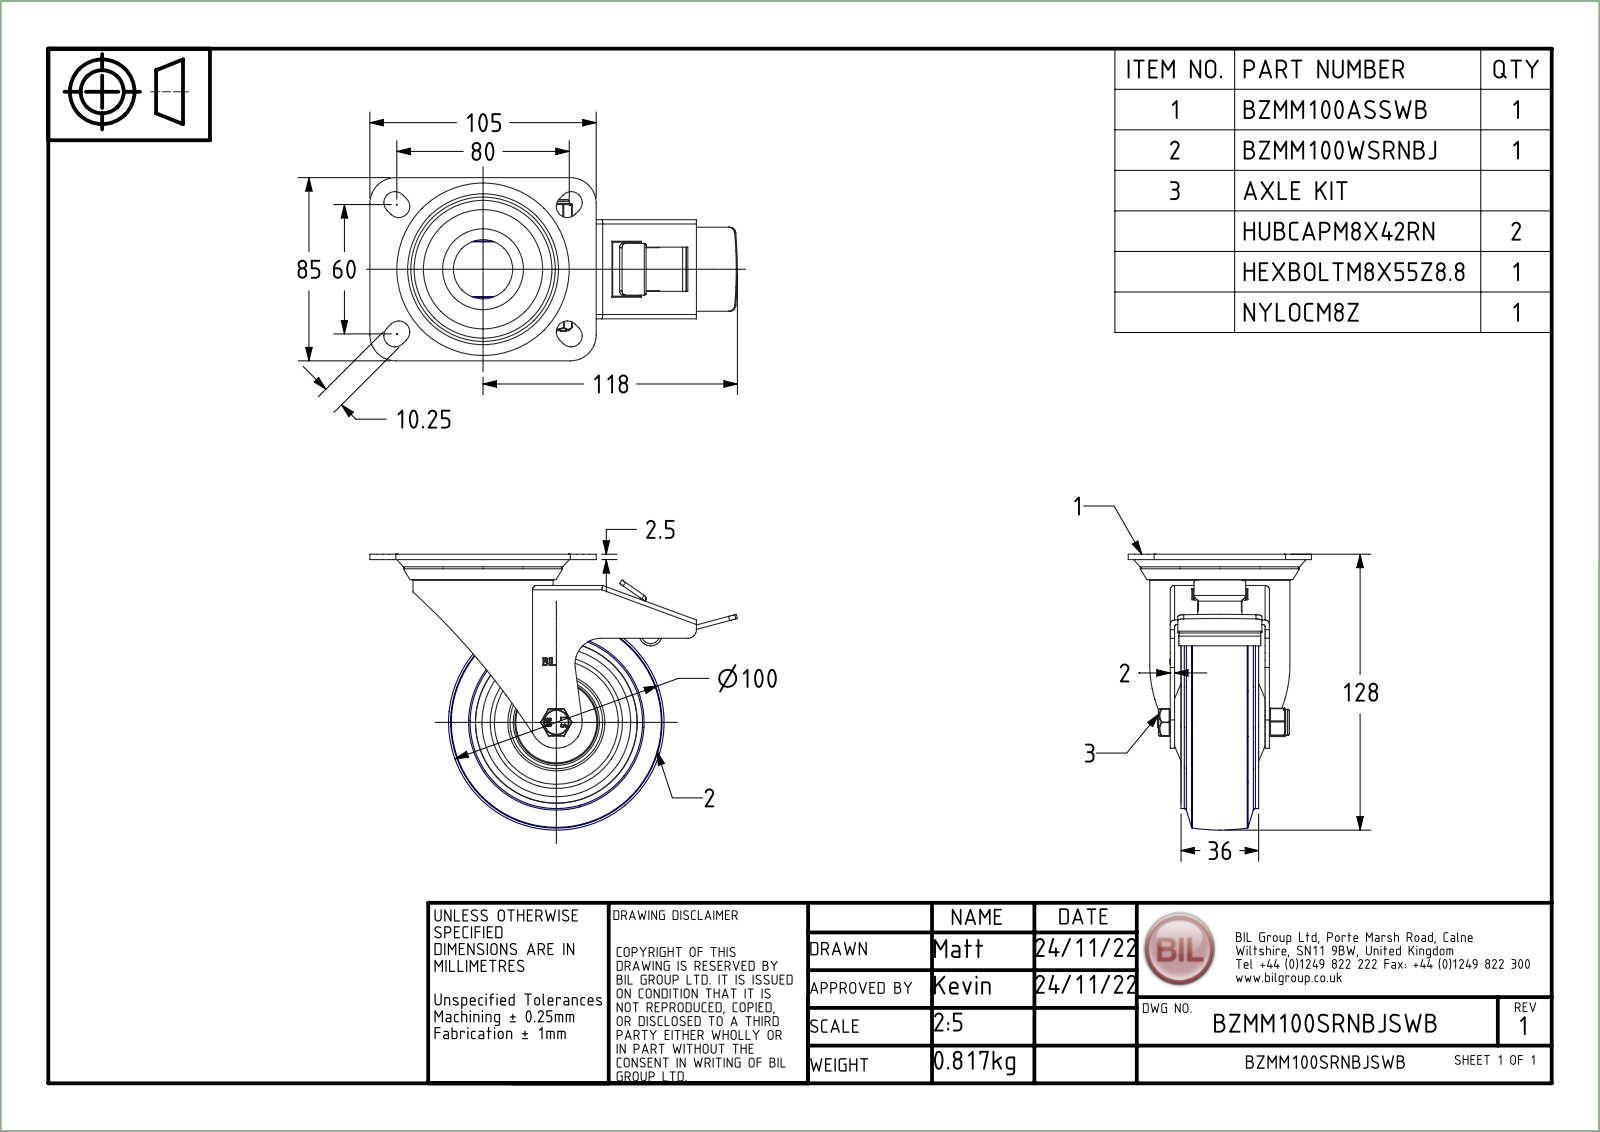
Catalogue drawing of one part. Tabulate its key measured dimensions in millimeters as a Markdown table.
| quantity | value |
| --- | --- |
| part name | BZMM100ASSWB 422; BRAKE PAD; ZINC PLATED, PRESSED STEEL TOP PLATE; ZINC PLATED, PRESSED STEEL TOP PLATE Geometry (+7 more) |
| STEP written by | Spatial InterOp 3D (AUTOMOTIVE_DESIGN) |
| units | millimeters |
| bodies | 49 solids, 1206 faces (428 planar, 364 cylindrical, 414 other) |
| overall size | 170.5 × 128 × 85 |
| volume | 256 448 mm³ |
| surface area | 146 887 mm² |
| round holes (diameter × count) | 0.66 × 2, 8 × 1, 8.2 × 1, 8.6 × 1, 15 × 1, 20 × 1, 22.5 × 1, 26 × 1, 27.5 × 1, 30 × 1, 31 × 1, 32 × 1 |
| round bosses / shafts (diameter × count) | 80 × 1, 65 × 1, 43 × 1, 38.5 × 1, 35 × 1, 31.5 × 1, 30.5 × 1, 28 × 1 |
| partial cylindrical surfaces (radius × count) | 0.5 × 22, 0.25 × 12, 2 × 9, 5.12 × 8, 1 × 6, 12 × 6, 0.33 × 4, 0.64 × 4 |
| main face-to-face distances | 2, 44, 3, 2.5, 1, 5, 18, 14.5, 26, 12.5 |
| hole center spacings | 3.22, 2.49 |
